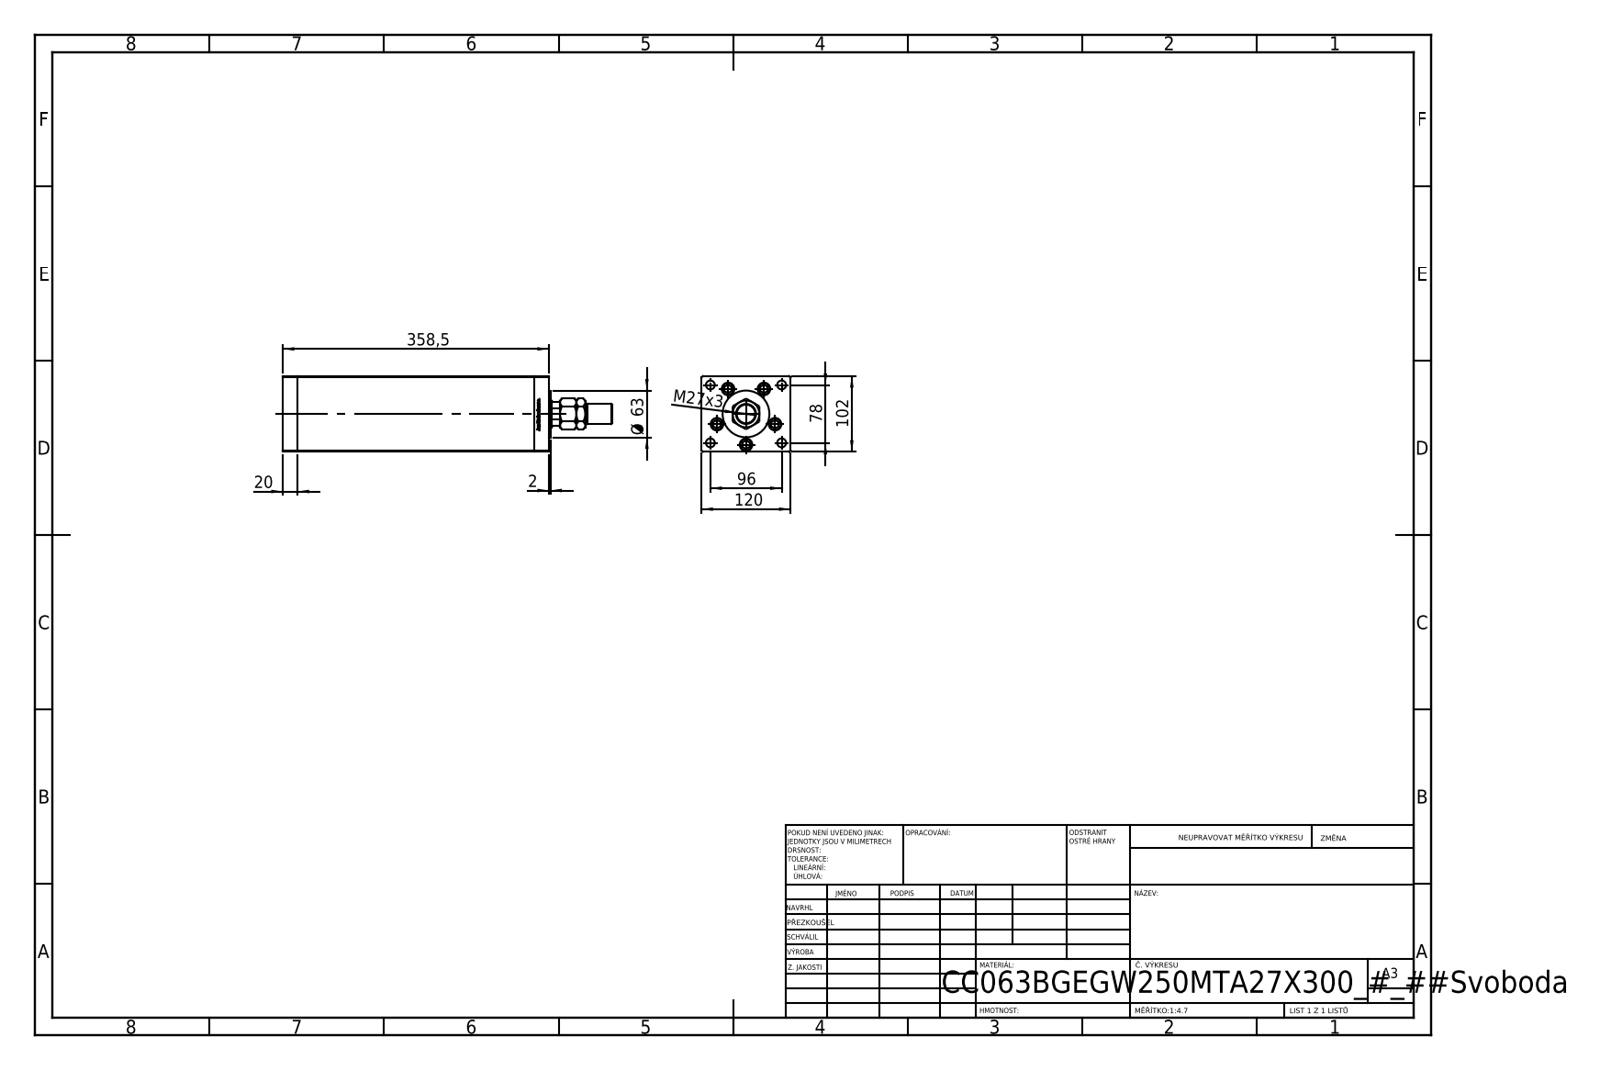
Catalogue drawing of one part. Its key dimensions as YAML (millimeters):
part_name: "ALLEN BOLT; MTA; V220C_VC_B; V220C BACK_B (+2 more)"
step_written_by: "SolidWorks 2019 (CONFIG_CONTROL_DESIGN)"
units: millimeters
bodies: {solids: 15, faces: 1234, planar: 479, cylindrical: 151, other: 604}
overall_size: [443.5, 120, 102]
volume: 3796000
surface_area: 397105
round_holes:
  - {diameter: 13.5, count: 5}
  - {diameter: 17, count: 5}
  - {diameter: 12, count: 4}
  - {diameter: 2, count: 2}
  - {diameter: 13.16, count: 2}
  - {diameter: 25.5, count: 1}
  - {diameter: 36, count: 1}
round_bosses_or_shafts:
  - {diameter: 8, count: 5}
  - {diameter: 63, count: 1}
  - {diameter: 27, count: 1}
  - {diameter: 25, count: 1}
partial_cylinders:
  - {radius: 0.93, count: 2}
  - {radius: 17.5, count: 1}
face_to_face_distances: [120, 102, 20, 318.5, 338.5, 34.25, 358.5, 14.25, 304.25, 324.25]
hole_center_spacings: [41.5, 61.85, 24.39, 26.69, 47.92, 48.07, 49.84, 53.57]
